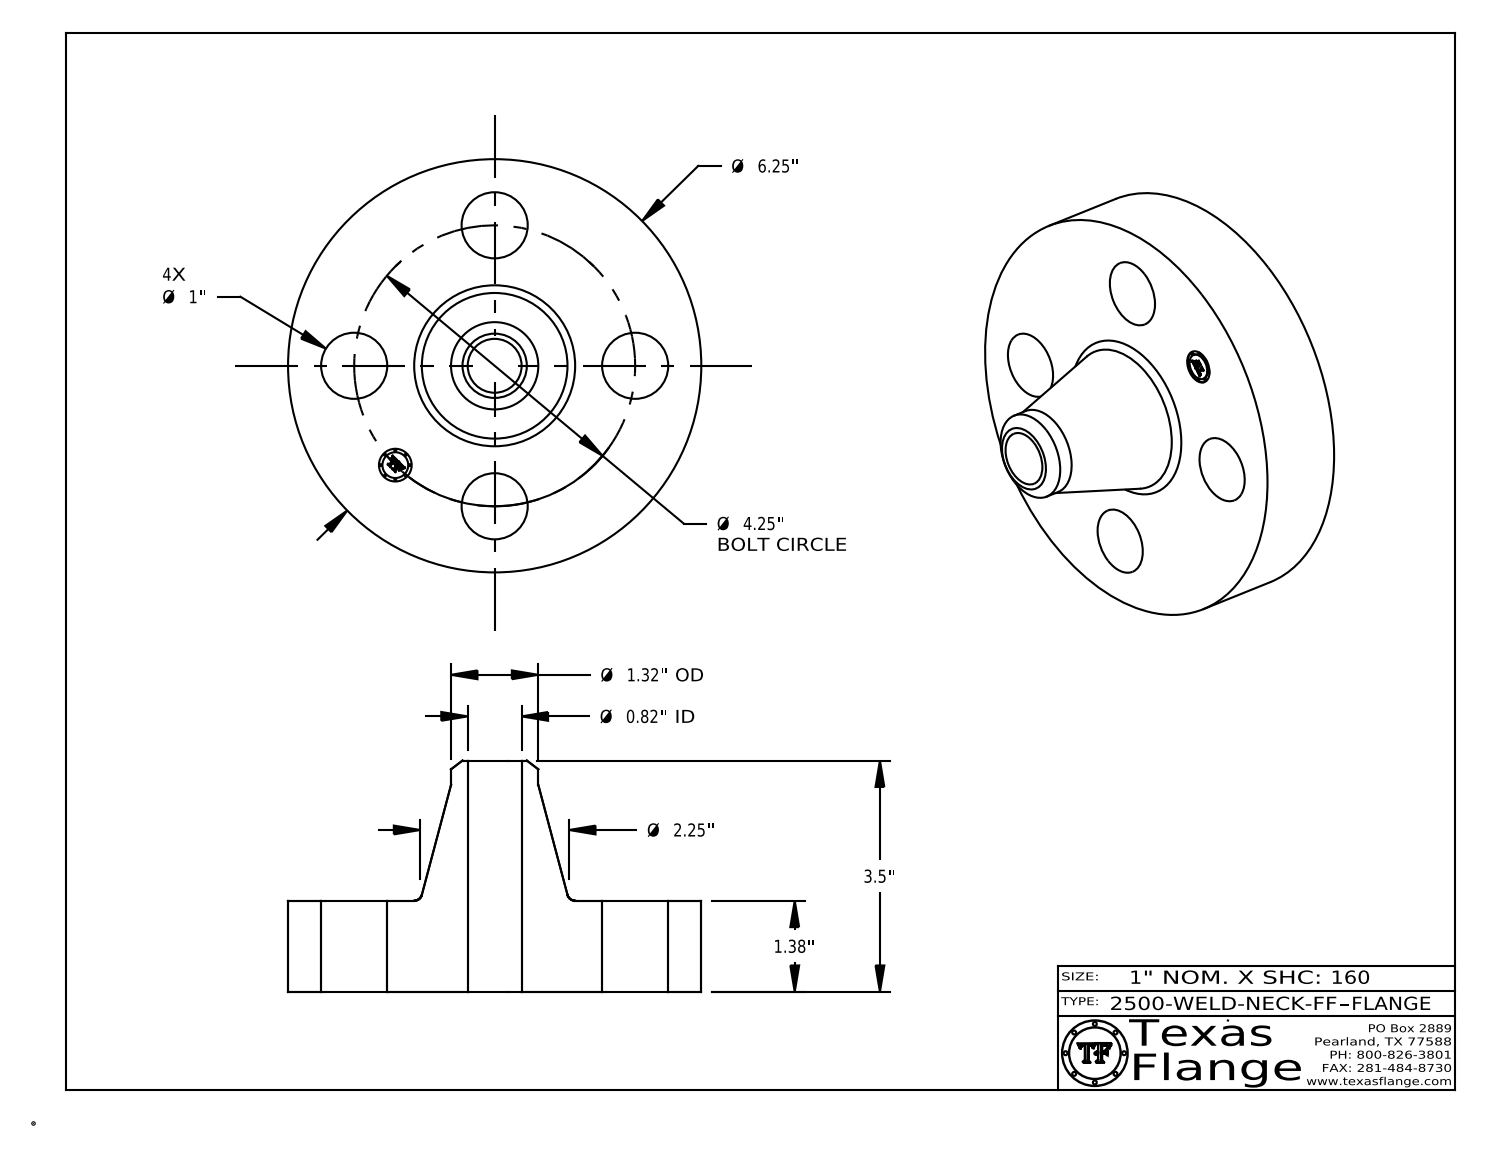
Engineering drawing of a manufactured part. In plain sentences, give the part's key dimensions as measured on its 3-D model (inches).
The part is named "2500-WELD-NECK-FF". Its 3-D file was written by "CATIA V5 STEP AP214 (AUTOMOTIVE_DESIGN)". It is 1 solid with 408 faces: 368 planar, 34 cylindrical and 6 other. Overall it measures 6.25 by 6.25 by 3.5 inches. Its volume is 41.13 cubic inches and its surface area 116 square inches. Round holes: 4 of diameter 1, 1 of diameter 0.495, 1 of diameter 0.815. Round bosses or shafts: 8 of diameter 0.03, 1 of diameter 6.25, 1 of diameter 1.32, 1 of diameter 0.39. The main face-to-face distances are 1.38, 3.5, 2.12, 1.365, 0.015, 2.135, 0.148, 0.144, 0.027, 0.096. The hole center spacings are 2.125, 3.006, 1.626, 3.927, 4.25.
